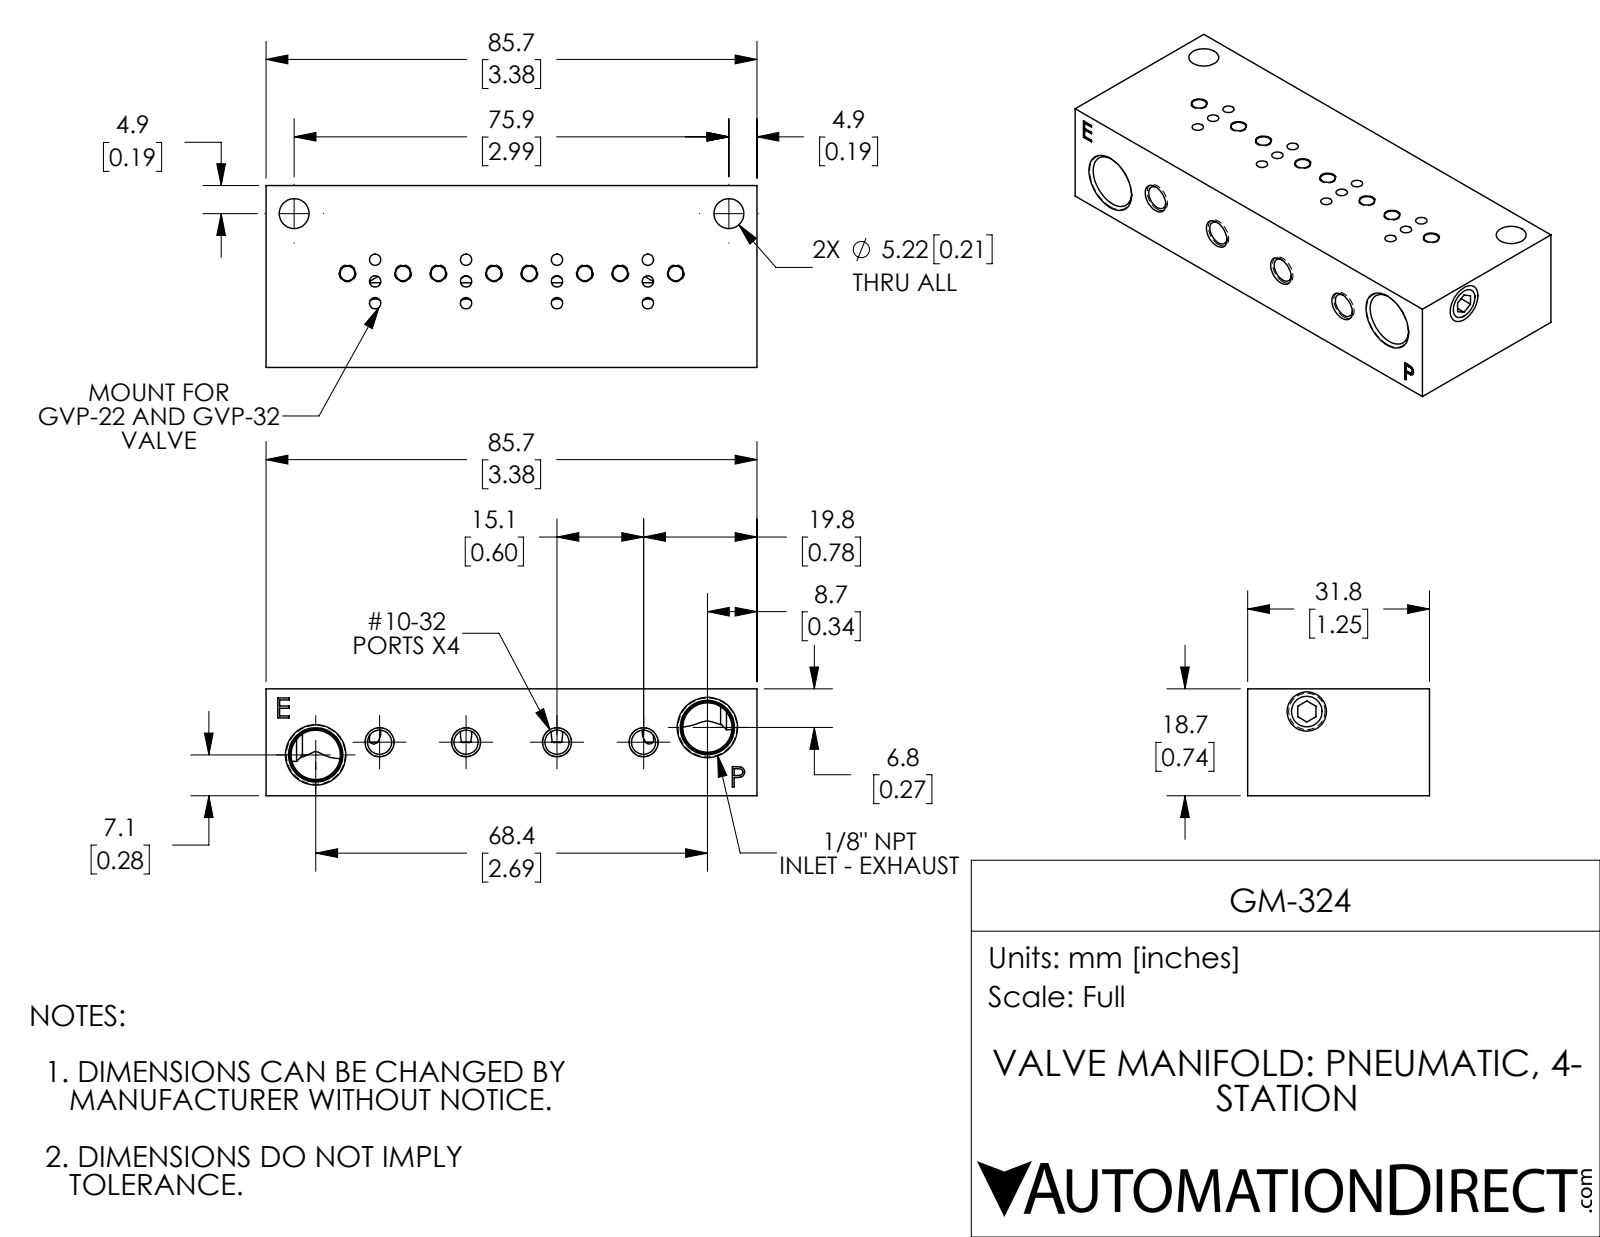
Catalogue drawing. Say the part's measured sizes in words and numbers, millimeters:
The part is named "GM-324". Its 3-D file was written by "SolidWorks 2018 (AUTOMOTIVE_DESIGN)". It is 3 solids with 220 faces: 49 planar, 65 cylindrical and 106 other. Overall it measures 85.7 by 31.8 by 18.7 millimeters. Its volume is 43 970 cubic millimeters and its surface area 15 260 square millimeters. Round holes: 12 of diameter 2, 8 of diameter 2.6, 4 of diameter 4.2, 2 of diameter 5.2, 2 of diameter 5.4, 2 of diameter 8.6. Round bosses or shafts: 2 of diameter 6.4. The main face-to-face distances are 18.7, 31.8, 85.7, 3.2, 4.1, 81.7, 79.4, 79.4, 3.2, 6.4. The hole center spacings are 31.8, 15.9, 5.1, 15.9, 5.4, 7.1, 12.2, 16.3.
